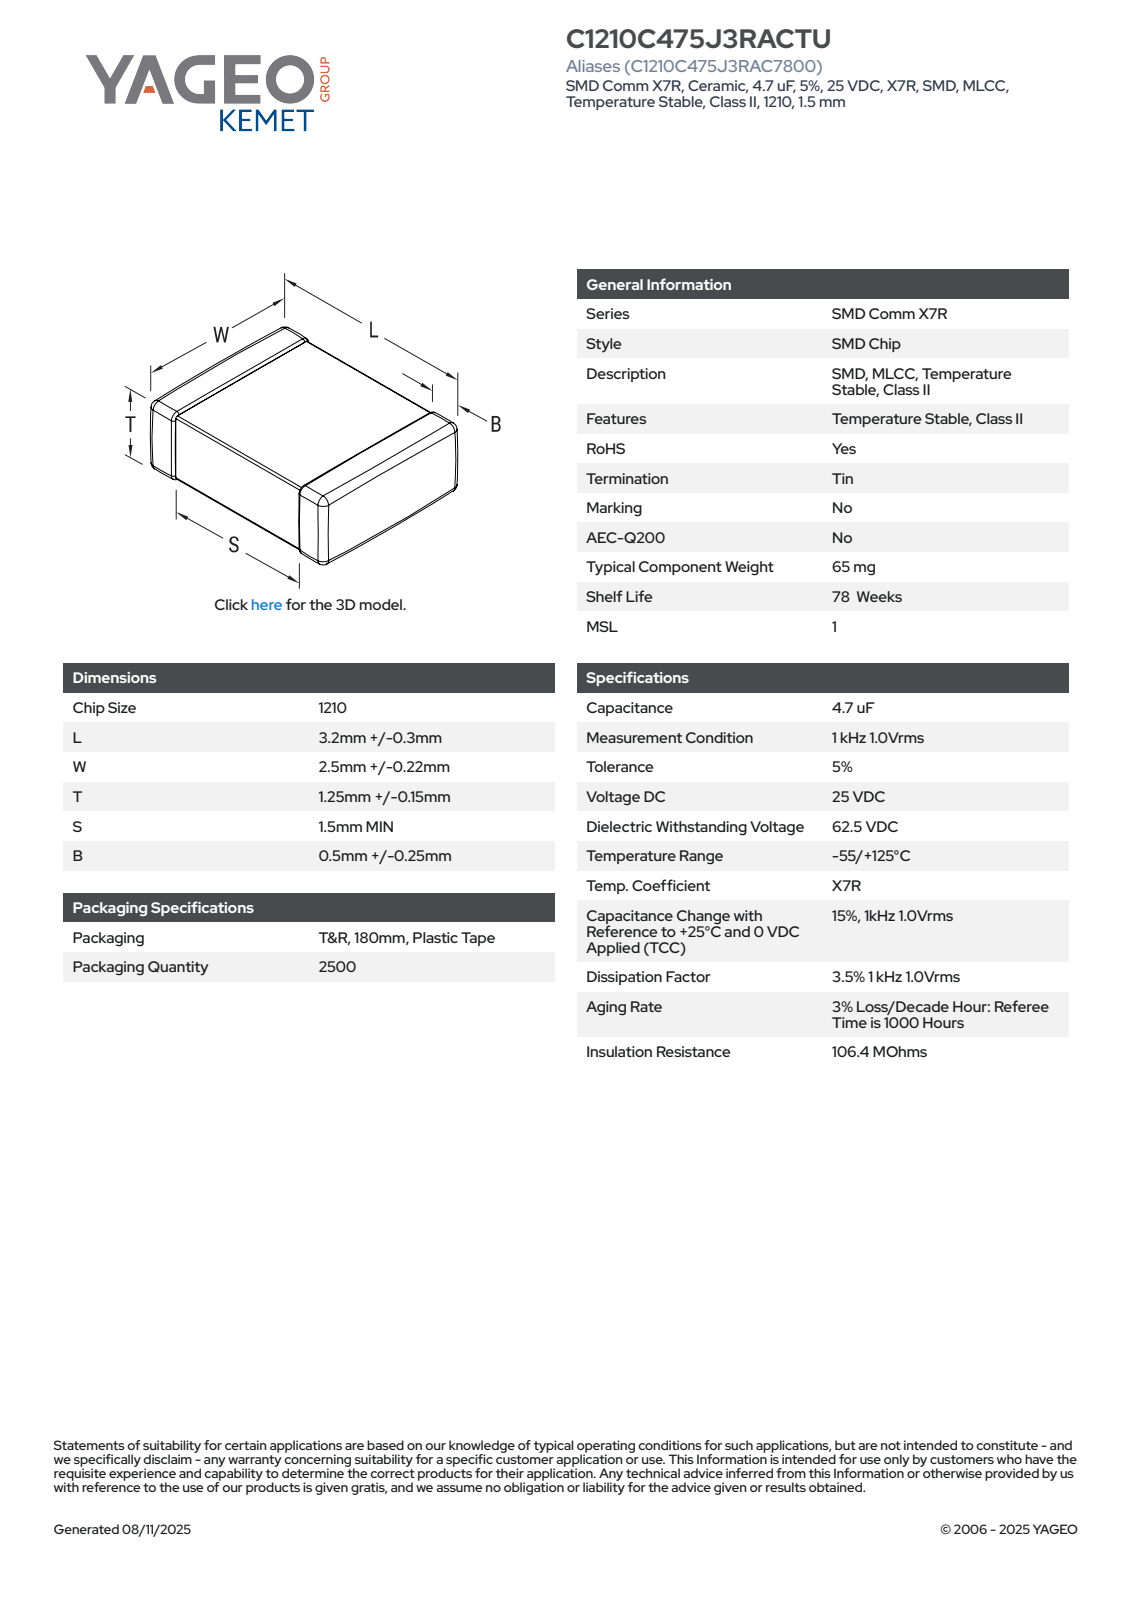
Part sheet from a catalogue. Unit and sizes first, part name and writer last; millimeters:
Units: millimetres
Overall size (bounding box): 3.5 × 2.72 × 1.4
Main face-to-face distances: 1.34, 1.28, 3.5, 1.4, 2.66, 2.6, 2.72, 1.35, 1.29, 1.49
Volume: 12 mm³ · Surface area: 36 mm²
Bodies: 4 solids, 125 faces (71 planar, 38 cylindrical, 16 other)
Part name (STEP PRODUCT): CCS_CCSTD_1210_L3.5W2.72T1.4B0.5
STEP written by: SolidWorks 2021 (AUTOMOTIVE_DESIGN)
